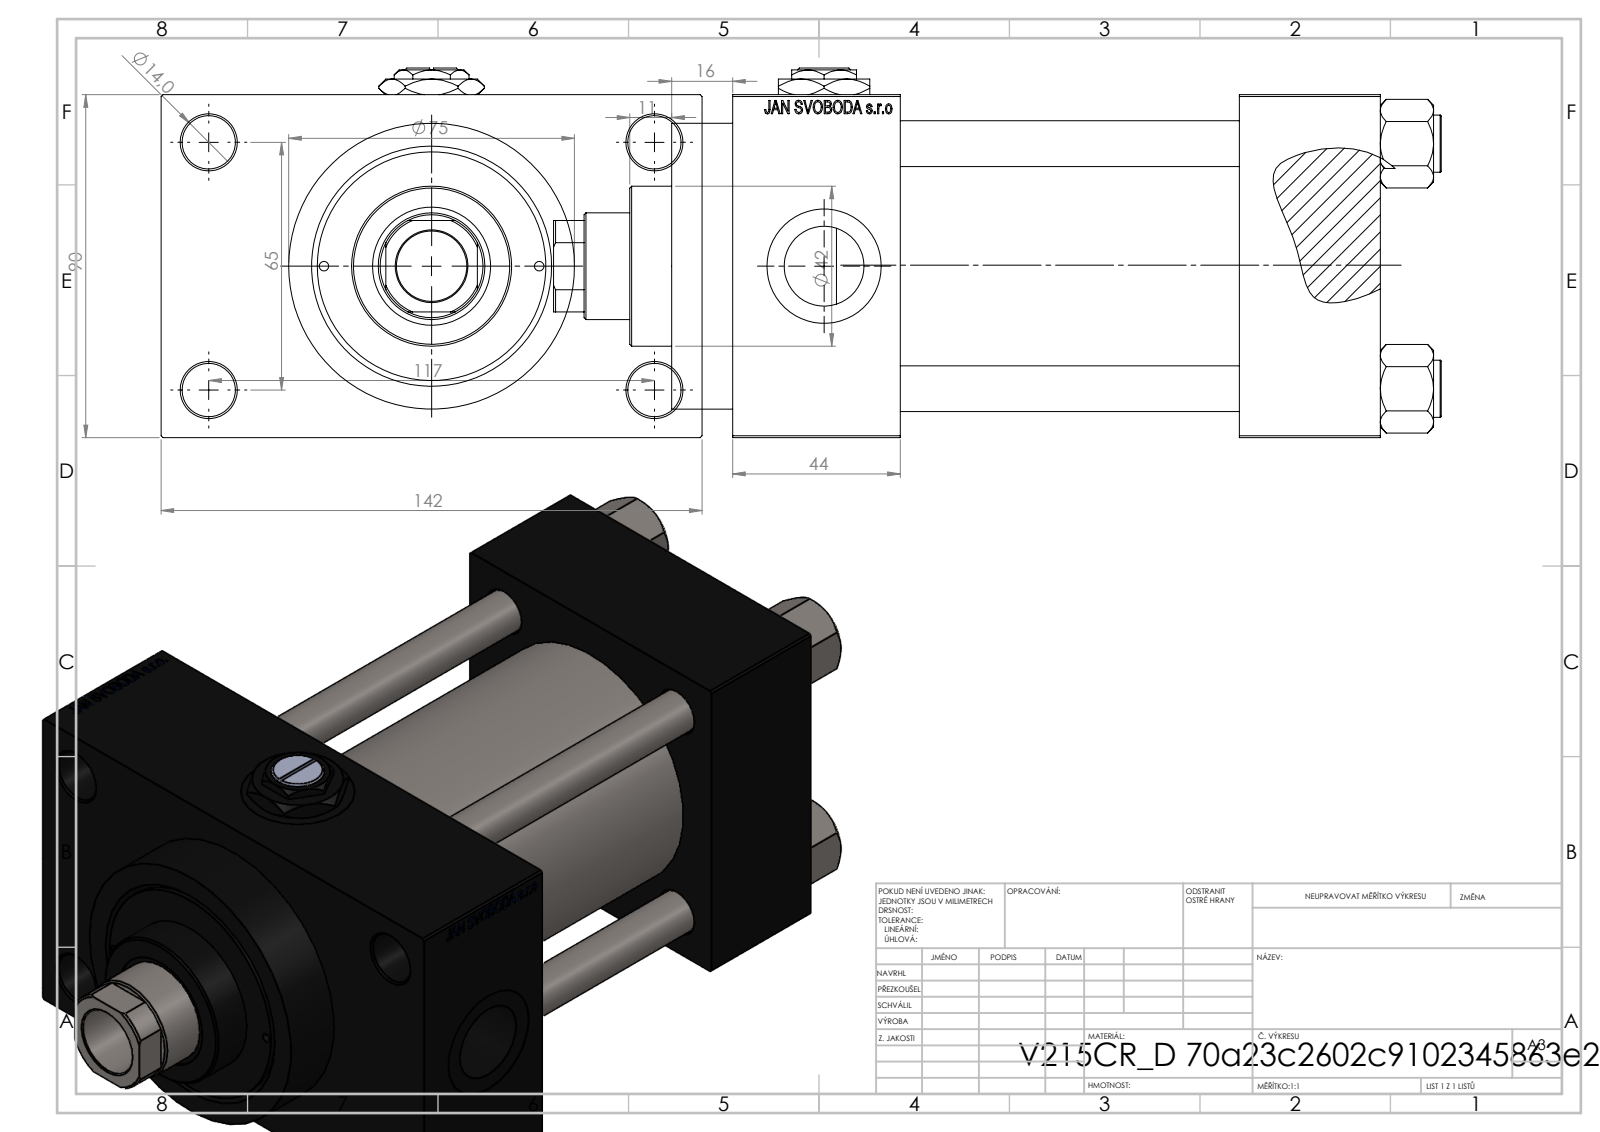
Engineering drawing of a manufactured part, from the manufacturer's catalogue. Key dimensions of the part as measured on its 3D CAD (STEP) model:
Part name (STEP PRODUCT): V215CR_VCP_D; NUT_M5_D; Zatka_pro_OIL_PORT; V215_VC_A (+2 more)
STEP written by: SolidWorks 2019 (CONFIG_CONTROL_DESIGN)
Units: millimetres
Bodies: 12 solids, 1159 faces (523 planar, 96 cylindrical, 540 other)
Overall size (bounding box): 233 × 142 × 97
Volume: 1 144 000 mm³ · Surface area: 221 689 mm²
Round holes (diameter × count): ⌀12 ×4, ⌀14 ×4, ⌀20.96 ×3, ⌀30 ×3, ⌀2.5 ×2, ⌀7 ×2, ⌀18.5 ×1, ⌀28 ×1, ⌀31 ×1, ⌀50 ×1, ⌀60 ×1, ⌀63 ×1
Round bosses / shafts (diameter × count): ⌀15 ×4, ⌀75 ×1, ⌀69 ×1, ⌀42 ×1
Partial cylindrical surfaces — rounded edges, fillets, slot ends (radius × count): R13.5 ×1
Main face-to-face distances: 90, 89, 37, 126, 133, 170, 44, 116, 26, 142
Hole centre spacings: 26.35, 32.39, 44.4, 45.47, 64.3, 66.92, 68.42, 69.81
